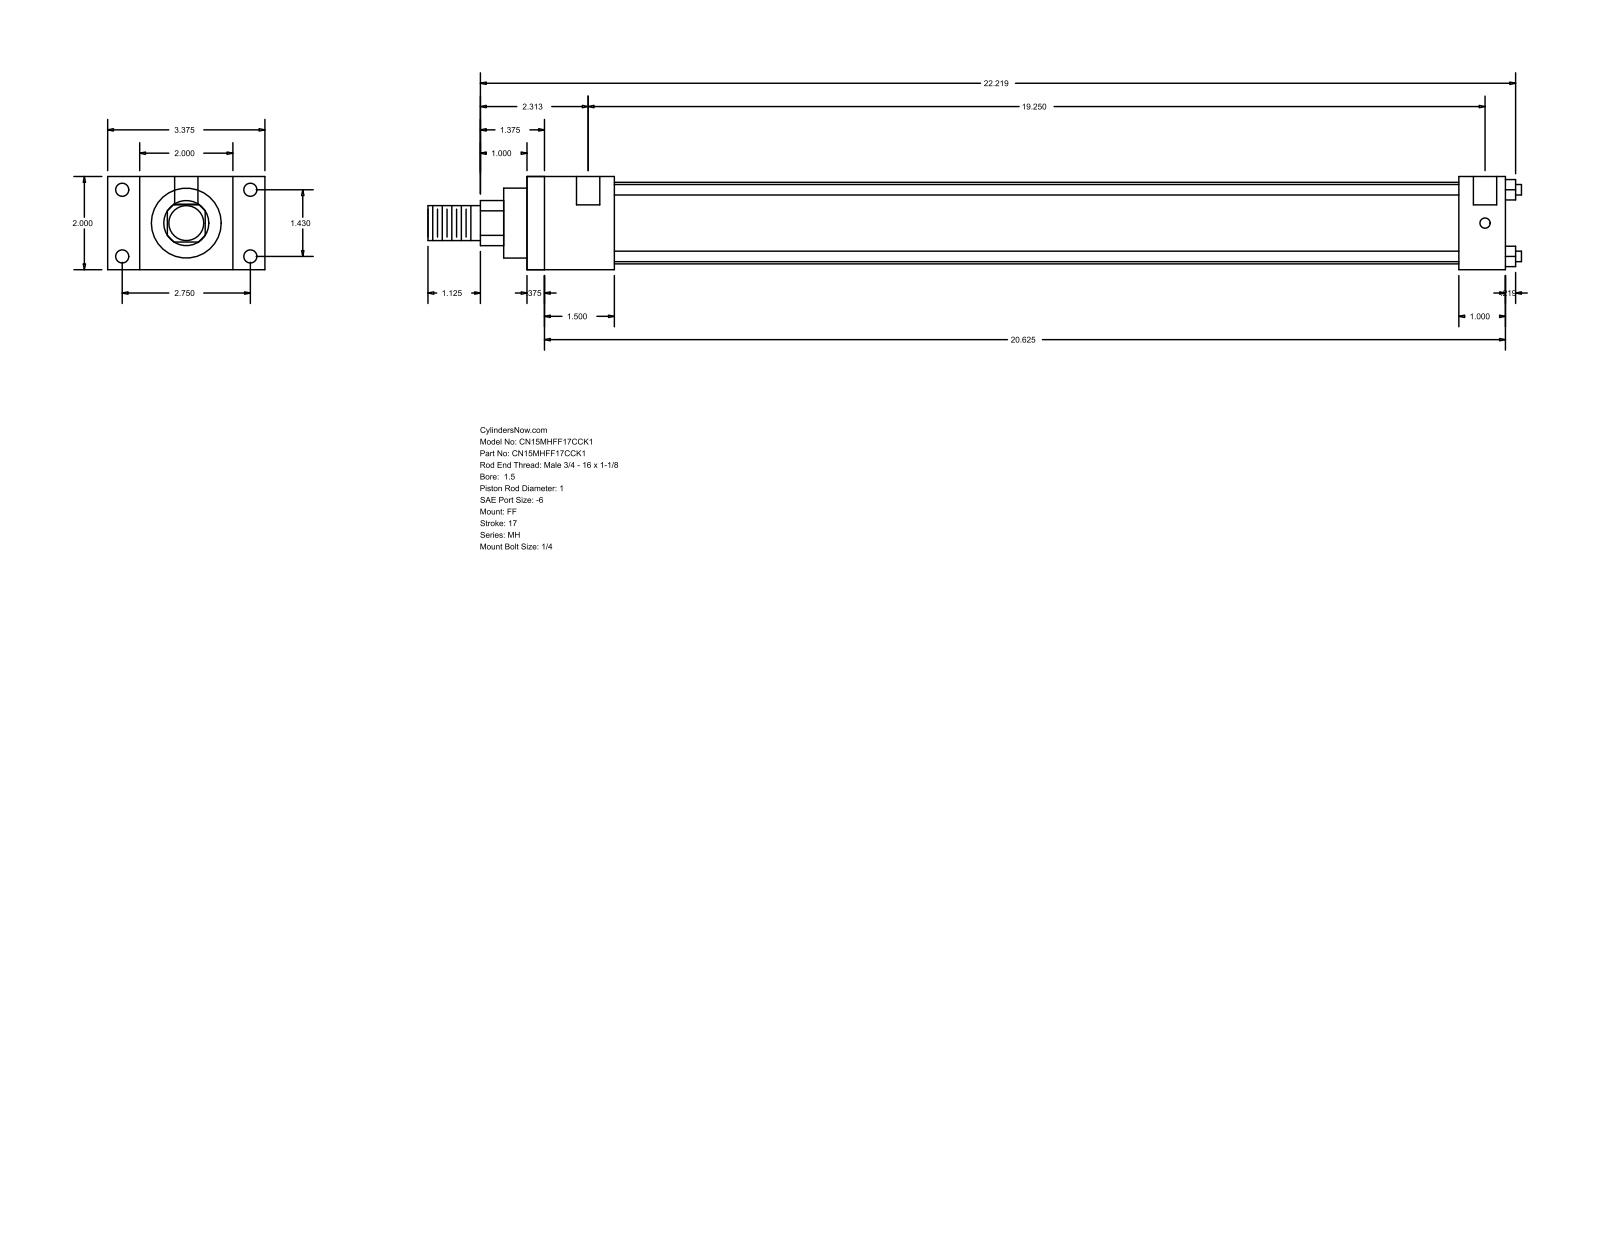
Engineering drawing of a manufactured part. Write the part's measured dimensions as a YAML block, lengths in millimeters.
part_name: "MH_FF__0150_1"
step_written_by: "GSSL Pune (CONFIG_CONTROL_DESIGN)"
units: millimeters
bodies: {solids: 0, faces: 92, planar: 64, cylindrical: 28, other: 0}
overall_size: [596.11, 85.72, 50.8]
round_holes:
  - {diameter: 5.56, count: 4}
  - {diameter: 7.14, count: 4}
  - {diameter: 12.7, count: 2}
round_bosses_or_shafts:
  - {diameter: 5.71, count: 4}
  - {diameter: 44.45, count: 1}
  - {diameter: 38.1, count: 1}
  - {diameter: 25.4, count: 1}
  - {diameter: 19.05, count: 1}
partial_cylinders:
  - {radius: 12.29, count: 1}
face_to_face_distances: [50.8, 533.4, 9.52, 523.88, 25.4, 17.46, 68.26, 47.63, 38.11, 485.77]
hole_center_spacings: [36.32, 69.84, 78.72, 492.13, 3.18, 488.95]
